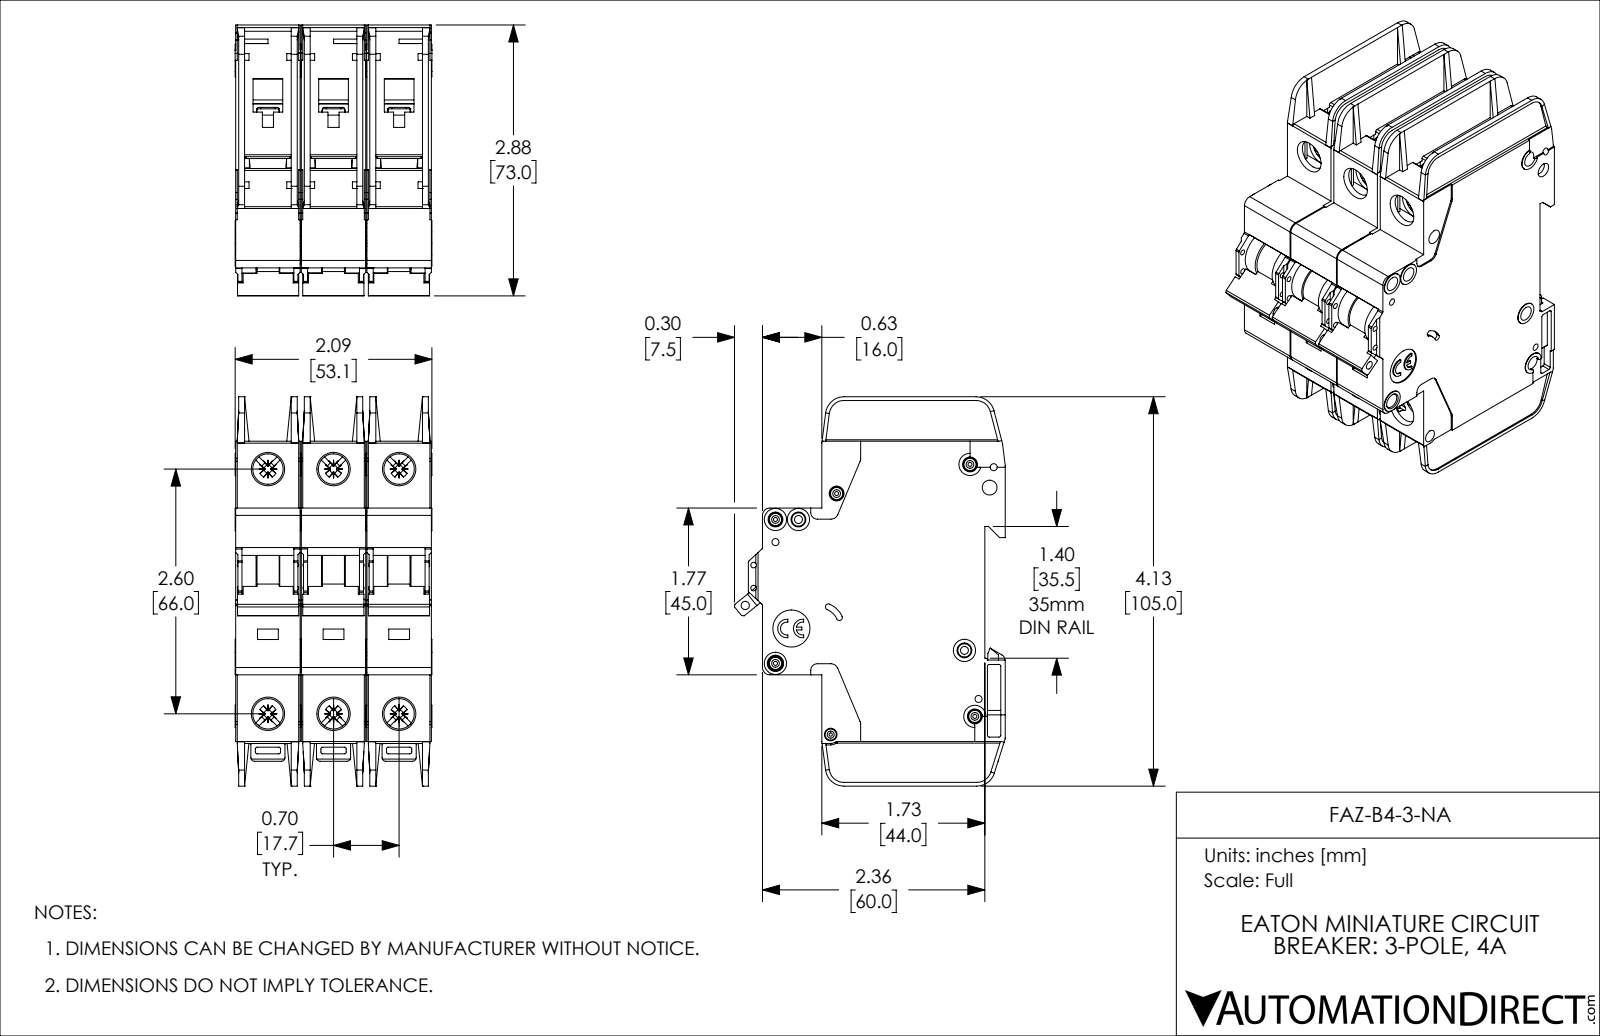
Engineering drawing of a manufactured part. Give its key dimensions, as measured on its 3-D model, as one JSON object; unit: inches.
{"part_name": "FAZ-B4-3-NA", "step_written_by": "SolidWorks 2019 (AUTOMOTIVE_DESIGN)", "units": "inches", "bodies": {"solids": 3, "faces": 3381, "planar": 2013, "cylindrical": 1071, "other": 297}, "overall_size": [4.134, 2.876, 2.091], "volume_in3": 14.05, "surface_area_in2": 123, "round_holes": [[0.157, 8], [0.323, 6], [0.043, 5], [0.075, 4], [0.059, 2], [0.085, 2], [0.035, 1], [0.089, 1], [0.098, 1], [0.134, 1], [0.394, 1]], "round_bosses_or_shafts": [[0.13, 5], [0.236, 4], [0.118, 4], [0.098, 3]], "partial_cylinders_radius": [[0.02, 72], [0.016, 30], [0.039, 18], [0.043, 12], [0.079, 12], [0.008, 6], [0.01, 6], [0.028, 6]], "face_to_face_distances": [0.697, 0.047, 1.394, 0.685, 0.591, 1.382, 0.744, 0.65, 0.106, 0.094], "hole_center_spacings": [0.697, 2.69, 2.598, 0.244, 0.537, 0.87, 1.394, 2.948]}
